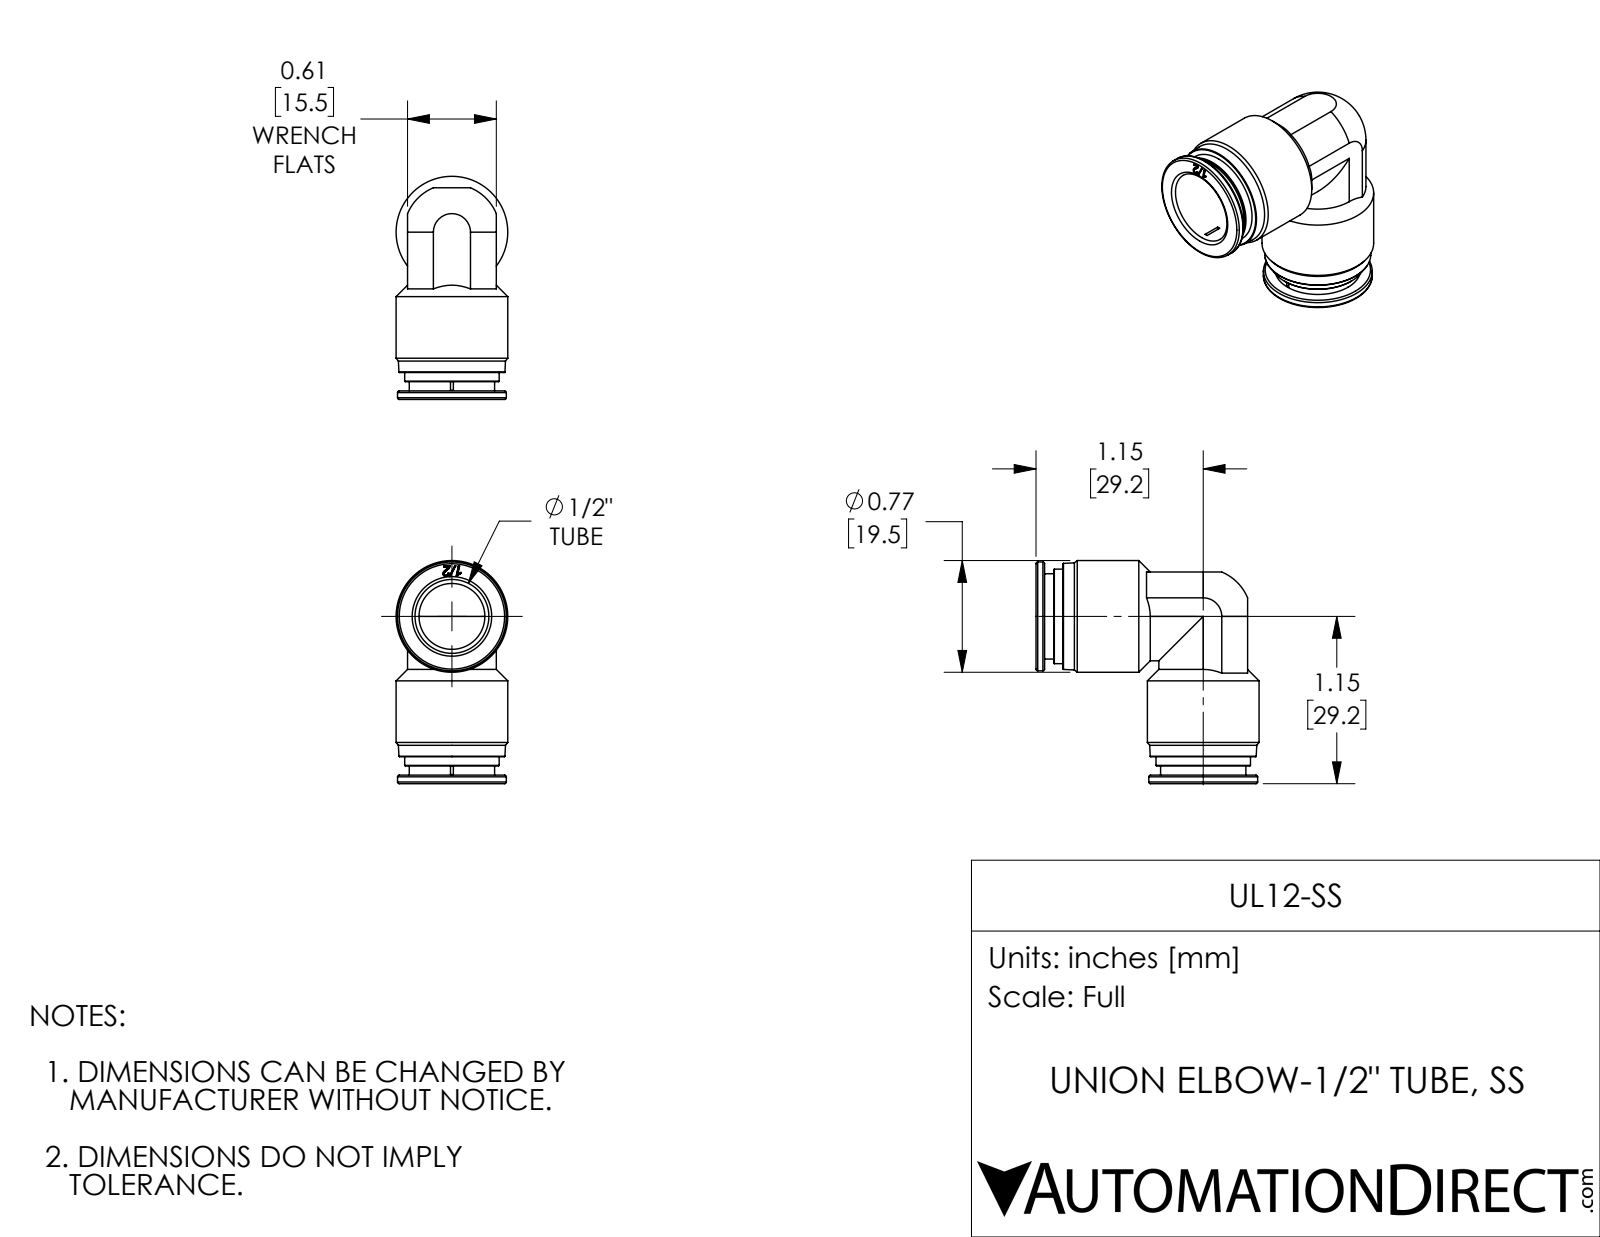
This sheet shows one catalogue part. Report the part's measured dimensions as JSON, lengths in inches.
{"part_name": "UL12-SS", "step_written_by": "SolidWorks 2017 (AUTOMOTIVE_DESIGN)", "units": "inches", "bodies": {"solids": 1, "faces": 167, "planar": 60, "cylindrical": 35, "other": 72}, "overall_size": [1.533, 1.533, 0.768], "volume_in3": 0.447, "surface_area_in2": 10.26, "round_holes": [[0.453, 2], [0.508, 2], [0.594, 2]], "round_bosses_or_shafts": [[0.768, 2], [0.748, 2], [0.65, 2], [0.587, 2]], "partial_cylinders_radius": [[0.305, 2], [0.331, 2]], "face_to_face_distances": [0.059, 1.455, 1.396, 0.185, 0.126, 1.27, 0.61, 0.063, 0.85, 0.791]}
